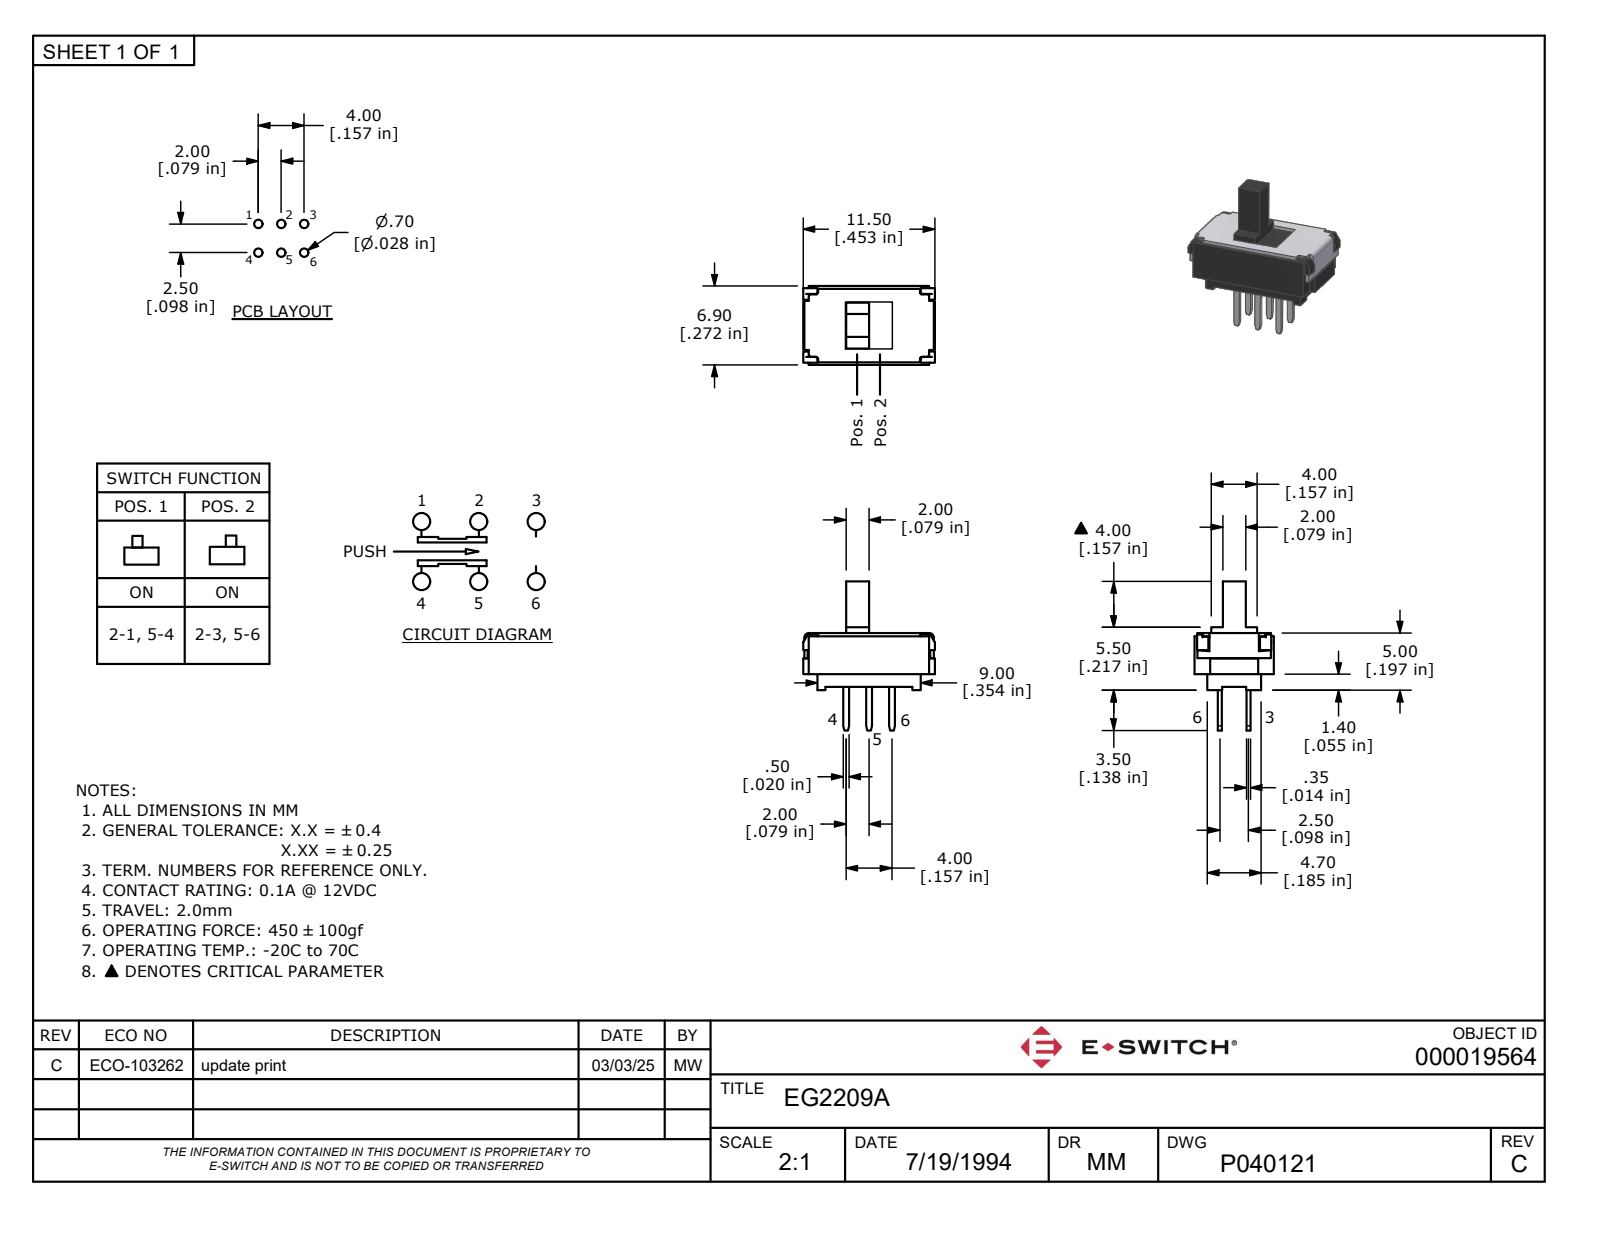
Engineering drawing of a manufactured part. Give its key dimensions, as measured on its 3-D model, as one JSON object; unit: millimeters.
{"part_name": "EG2209A", "step_written_by": "Autodesk Inventor 2020 (AUTOMOTIVE_DESIGN)", "units": "millimeters", "bodies": {"solids": 0, "faces": 163, "planar": 157, "cylindrical": 6, "other": 0}, "overall_size": [13, 11.5, 6.9], "partial_cylinders_radius": [[0.1, 2], [0.4, 2]], "face_to_face_distances": [1.1, 4.7, 3.6, 6.9, 2, 0.5, 2.5, 5.75, 5.8, 1.35]}
